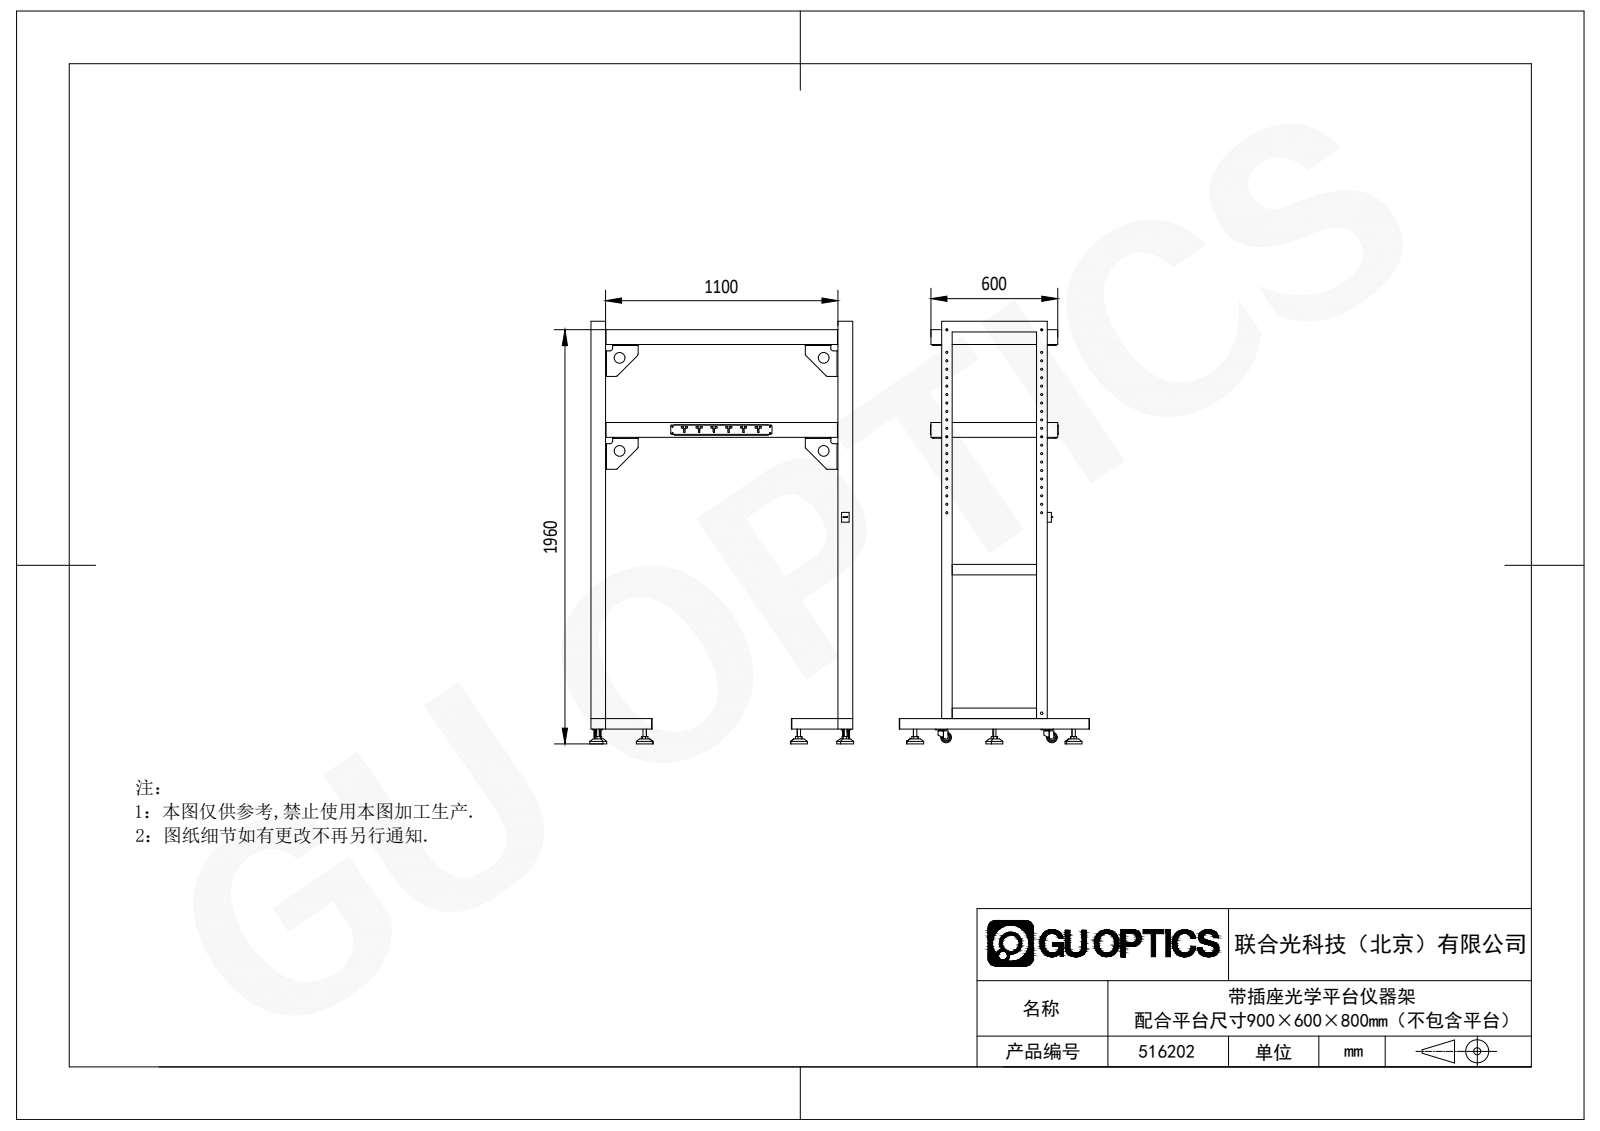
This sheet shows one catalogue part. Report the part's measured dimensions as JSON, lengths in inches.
{"part_name": "516202", "step_written_by": "SolidWorks 2020 (CONFIG_CONTROL_DESIGN)", "units": "inches", "bodies": {"solids": 53, "faces": 2181, "planar": 1133, "cylindrical": 972, "other": 76}, "overall_size": [78.78, 49.213, 35.433], "volume_in3": 1037, "surface_area_in2": 18430, "round_holes": [[0.354, 66], [0.24, 16], [0.394, 16], [0.165, 8], [0.256, 6], [0.669, 6], [0.709, 6], [1.024, 6], [2.717, 6], [0.126, 4], [0.205, 4], [0.236, 4]], "round_bosses_or_shafts": [[3.15, 6], [0.63, 6], [1.024, 4], [0.709, 4], [1.969, 2], [0.394, 2]], "partial_cylinders_radius": [[0.197, 28], [0.276, 24], [0.118, 16], [0.059, 8], [0.059, 8], [0.158, 8], [0.167, 6], [0.512, 4]], "face_to_face_distances": [0.079, 0.118, 1.969, 17.323, 2.756, 0.059, 46.063, 17.717, 1.89, 2.638], "hole_center_spacings": [1.575, 3.15, 4.724, 6.299, 7.874, 11.024, 9.449, 12.598]}
